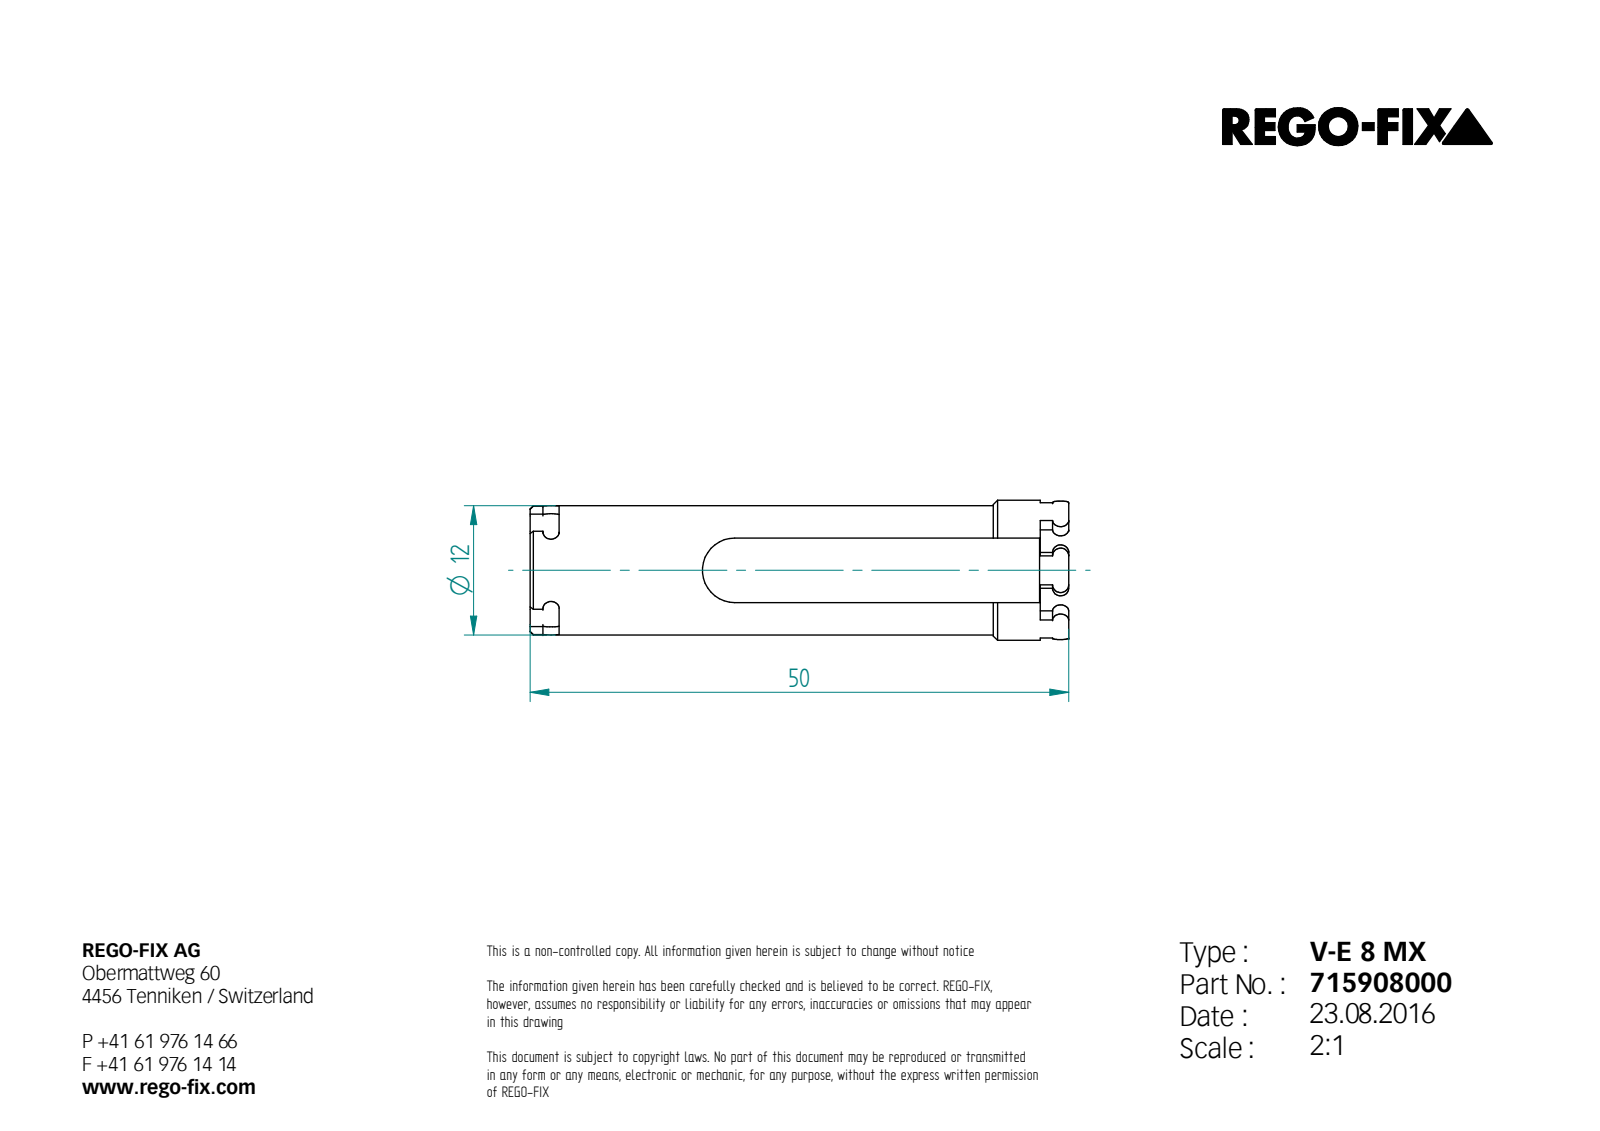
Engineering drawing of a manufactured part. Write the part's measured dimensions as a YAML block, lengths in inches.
step_written_by: "Unknown (AUTOMOTIVE_DESIGN)"
units: inches
bodies: {solids: 1, faces: 99, planar: 61, cylindrical: 28, other: 10}
overall_size: [1.969, 0.512, 0.492]
volume: 0.146
surface_area: 4.752
round_holes:
  - {diameter: 0.354, count: 1}
  - {diameter: 0.417, count: 1}
round_bosses_or_shafts:
  - {diameter: 0.512, count: 1}
  - {diameter: 0.472, count: 1}
partial_cylinders:
  - {radius: 0.03, count: 12}
  - {radius: 0.118, count: 1}
  - {radius: 0.14, count: 1}
  - {radius: 0.205, count: 1}
face_to_face_distances: [0.257, 0.247, 0.236, 1.862, 1.864, 0.106, 0.346, 1.758, 1.756, 0.104]
